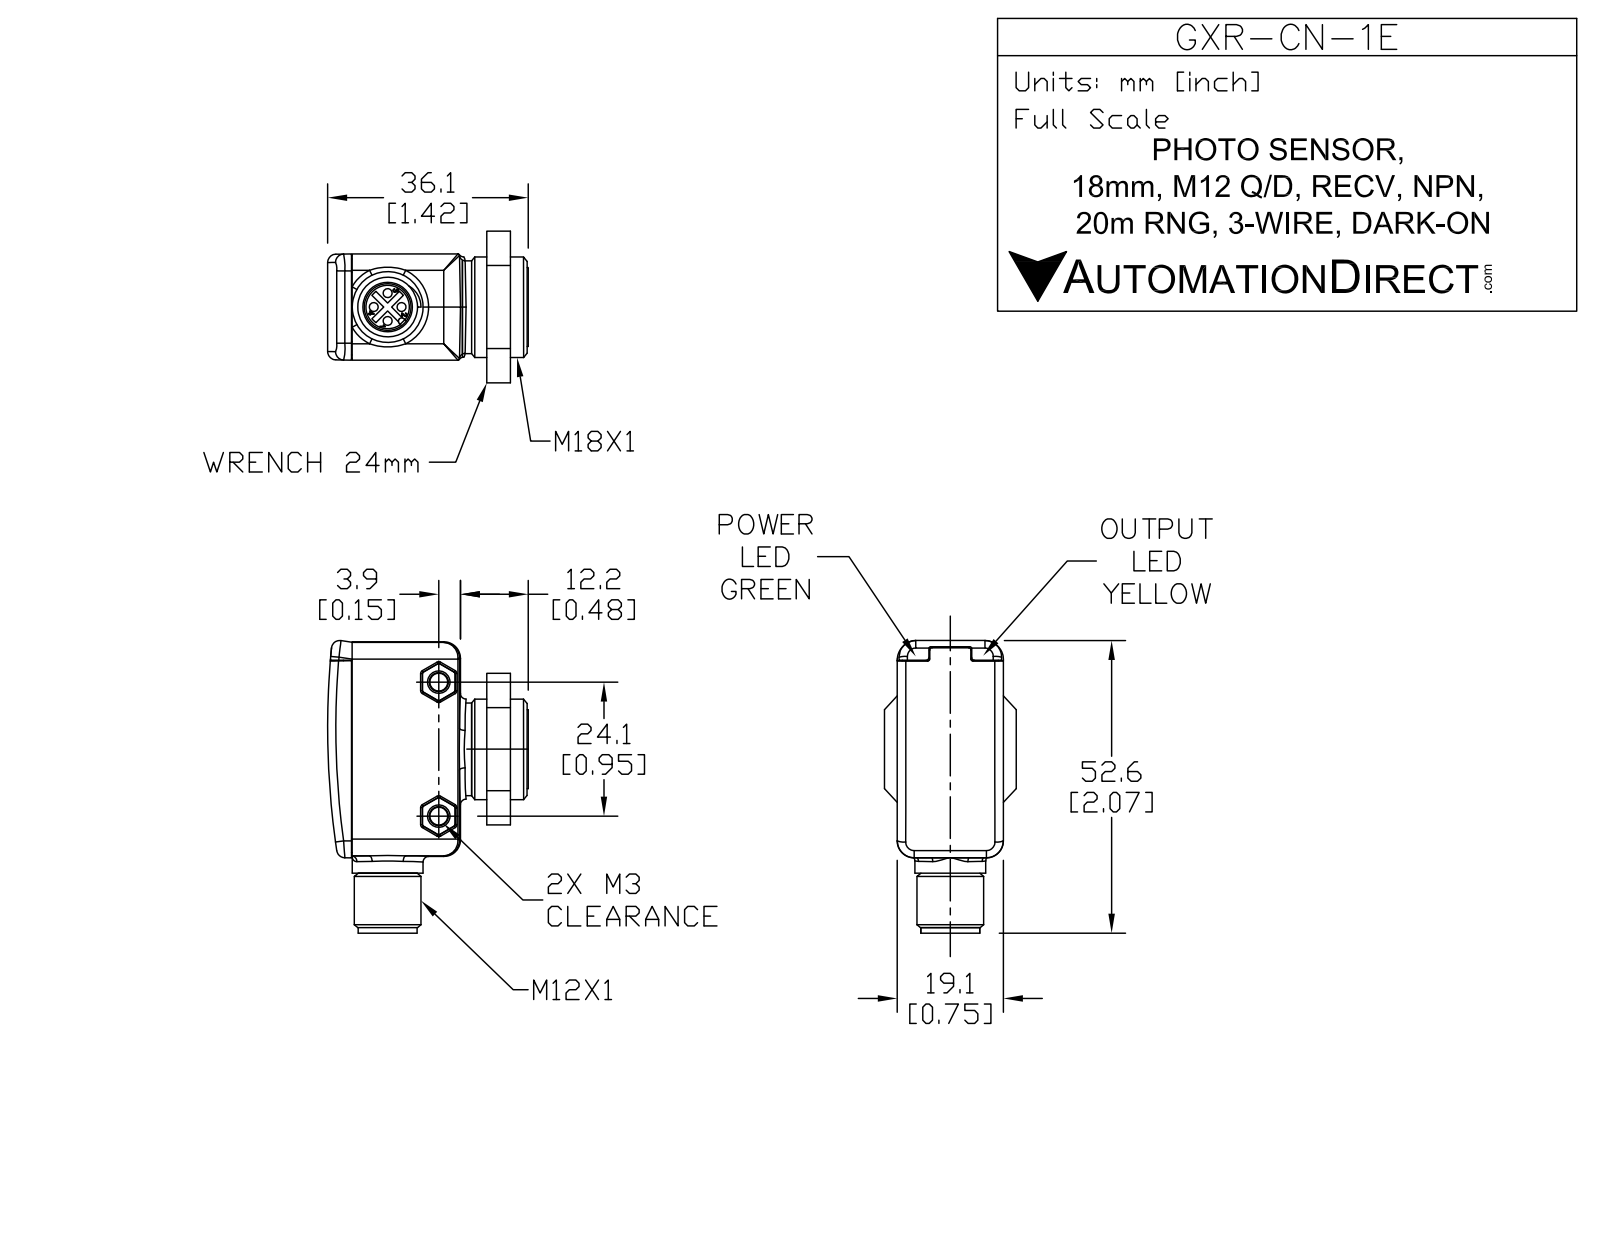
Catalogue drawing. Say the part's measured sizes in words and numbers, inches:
The part is named "GXR-CN-1E". Its 3-D file was written by "SolidWorks 2013 (AUTOMOTIVE_DESIGN)". It is 1 solid with 107 faces: 60 planar, 33 cylindrical and 14 other. Overall it measures 2.073 by 1.421 by 0.939 inches. Its volume is 1.297 cubic inches and its surface area 10 square inches. Round holes: 2 of diameter 0.126, 1 of diameter 0.329. Round bosses or shafts: 1 of diameter 0.709, 1 of diameter 0.689, 1 of diameter 0.559, 1 of diameter 0.499, 1 of diameter 0.455, 1 of diameter 0.417. Partial cylindrical surfaces (rounded edges, fillets, slot ends): 8 of radius 0.059, 4 of radius 0.039, 1 of radius 5.495. The main face-to-face distances are 0.752, 0.283, 0.083, 0.367, 0.756, 0.197, 0.113, 0.48, 1.528, 0.234. The hole center spacings are 0.949.
